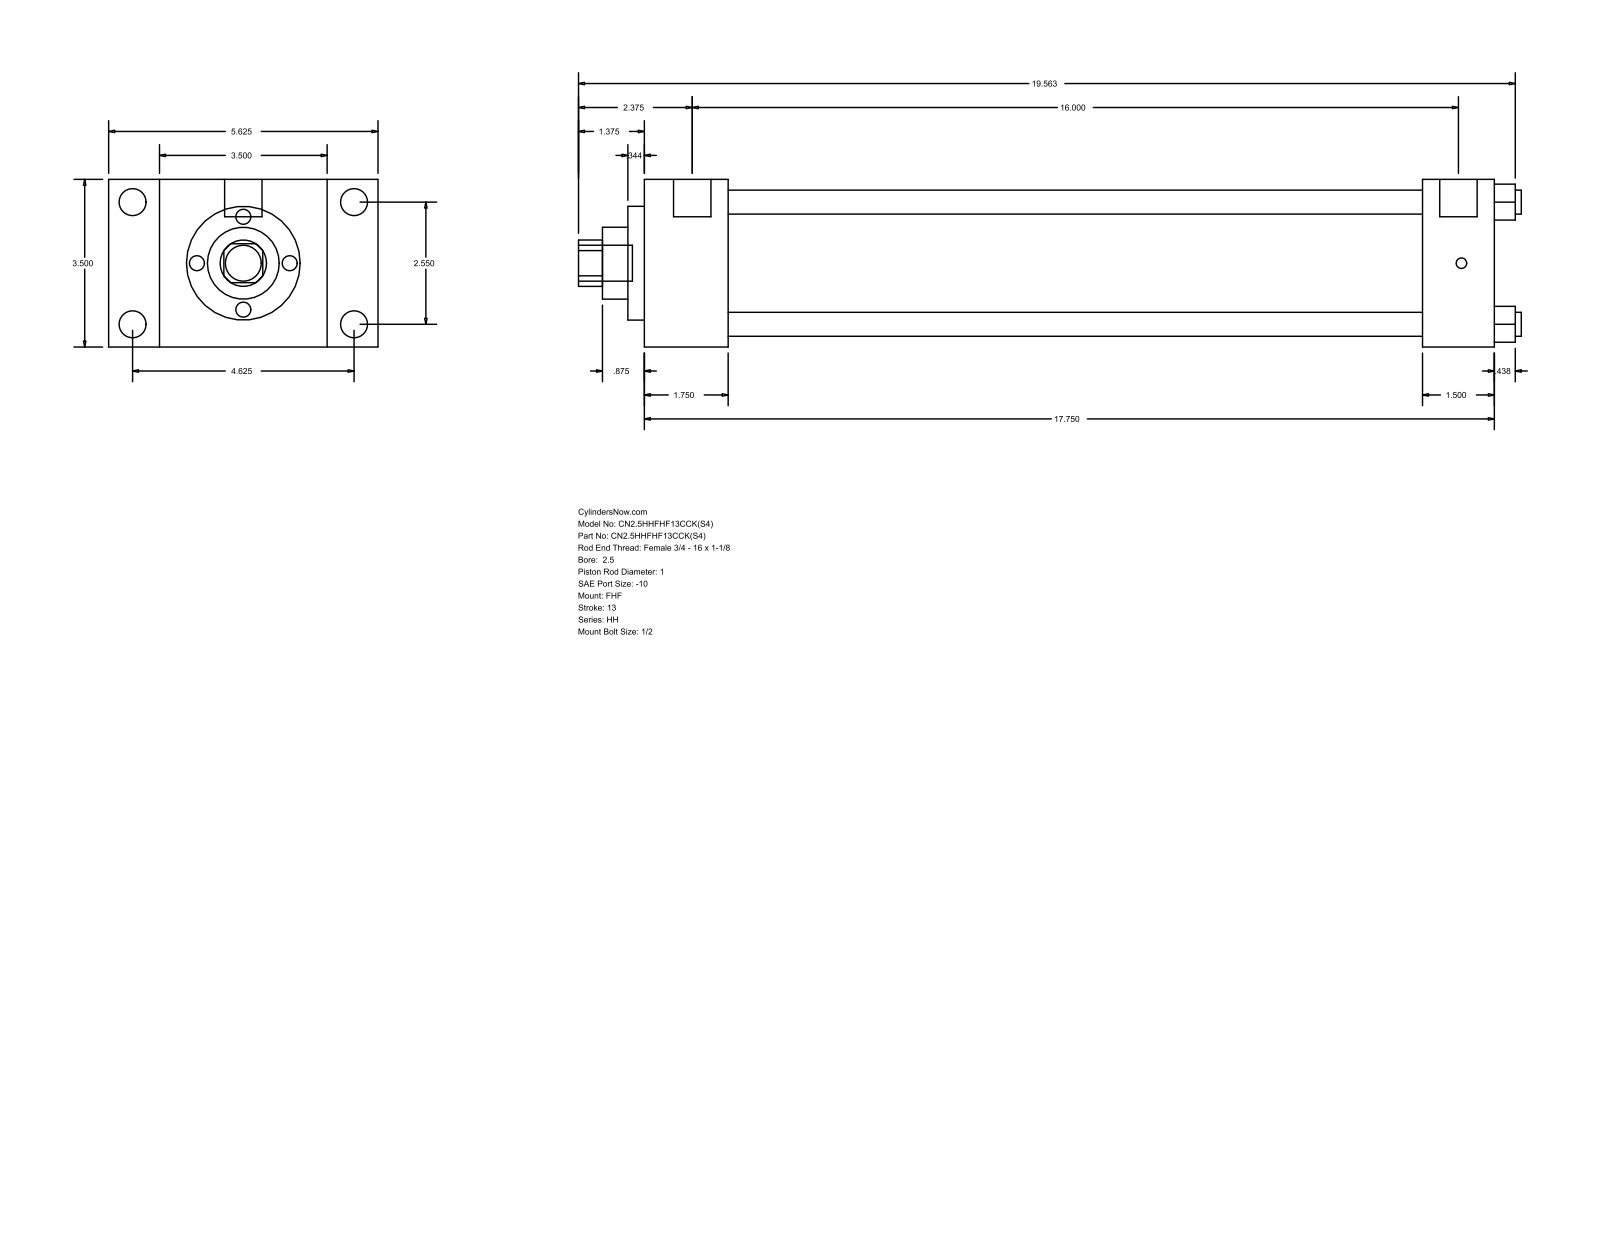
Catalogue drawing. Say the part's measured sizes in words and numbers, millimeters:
The part is named "HH_FHF__0250_1". Its 3-D file was written by "GSSL Pune (CONFIG_CONTROL_DESIGN)". It is 0 solids with 90 faces: 61 planar, 29 cylindrical and 0 other. Overall it measures 500.06 by 142.88 by 88.9 millimeters. Round holes: 4 of diameter 12.7, 1 of diameter 25.4, 1 of diameter 38.1, 1 of diameter 60.33, 1 of diameter 73.03. Round bosses or shafts: 4 of diameter 14.3, 4 of diameter 5.56, 2 of diameter 19.84, 1 of diameter 19.05. Partial cylindrical surfaces (rounded edges, fillets, slot ends): 1 of radius 12.29. The main face-to-face distances are 88.9, 44.46, 26.99, 115.89, 450.85, 406.39, 142.88, 412.76, 368.3, 38.09. The hole center spacings are 45.79, 64.76, 91.58.
